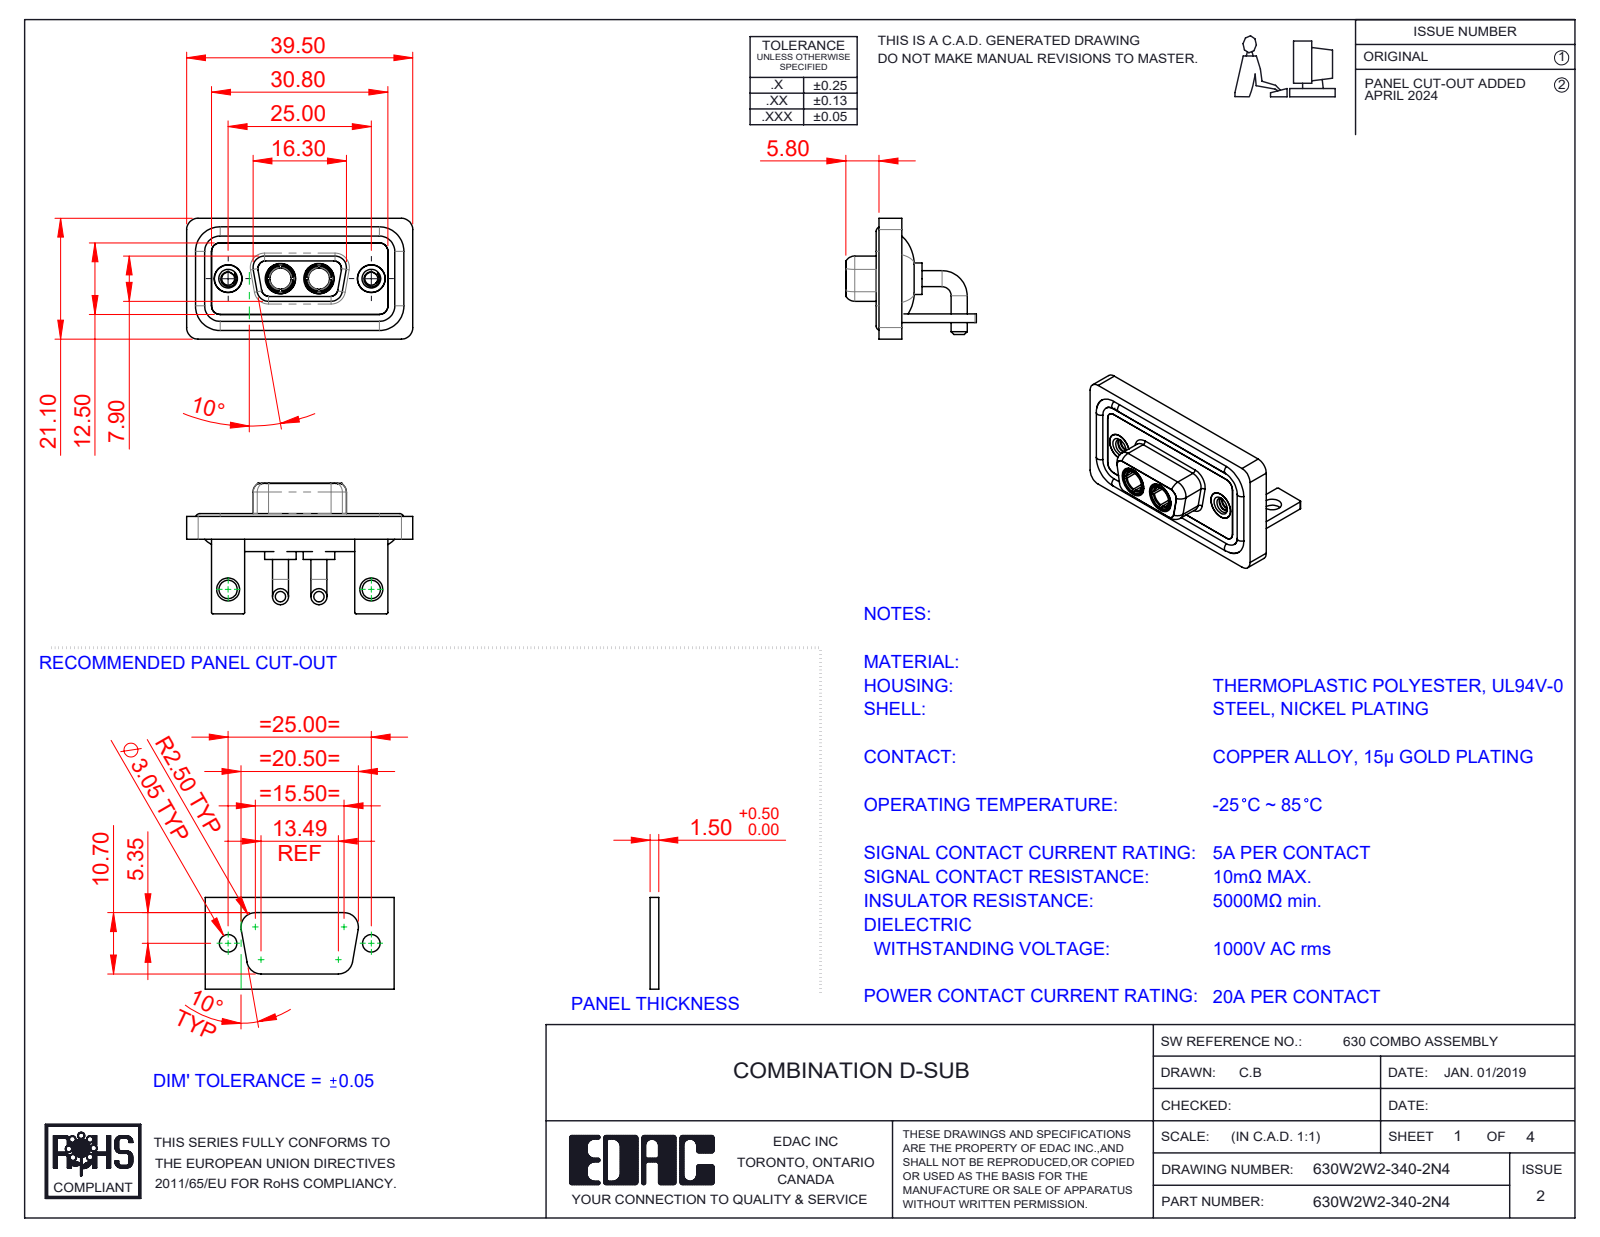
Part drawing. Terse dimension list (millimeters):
name: 630Combo Waterproof Housing_09 Contacts; 630Combo Shell Front_09 Contacts; Power Socket_20A RA; 630Combo Housing_2W2 (+4 more)
written by: SolidWorks 2023 (CONFIG_CONTROL_DESIGN)
unit: mm
bodies: 13 solids, 590 faces (183 planar, 262 cylindrical, 145 other)
size: 39.5 × 22.8 × 21.1
volume: 5 182 mm³; area: 8 521 mm²
holes: 4× ⌀4.85, 2× ⌀2.26, 2× ⌀3.2, 2× ⌀3.7, 2× ⌀4, 2× ⌀4.05, 2× ⌀5, 2× ⌀5.3
bosses: 4× ⌀2.8, 4× ⌀1.6, 2× ⌀5.5, 2× ⌀5.2, 2× ⌀4.96, 2× ⌀4.95, 2× ⌀4.8, 2× ⌀4.75
rounds: 19× R2, 18× R1.5, 16× R0.25, 8× R1.35, 8× R1.6, 5× R0.5, 4× R0.6, 4× R0.65
face distances: 0.4, 2.9, 1.5, 1.8, 1.1, 3.7, 0.8, 2.5, 1.6, 3.1
hole spacings: 9.14, 15.86, 25, 6.72
